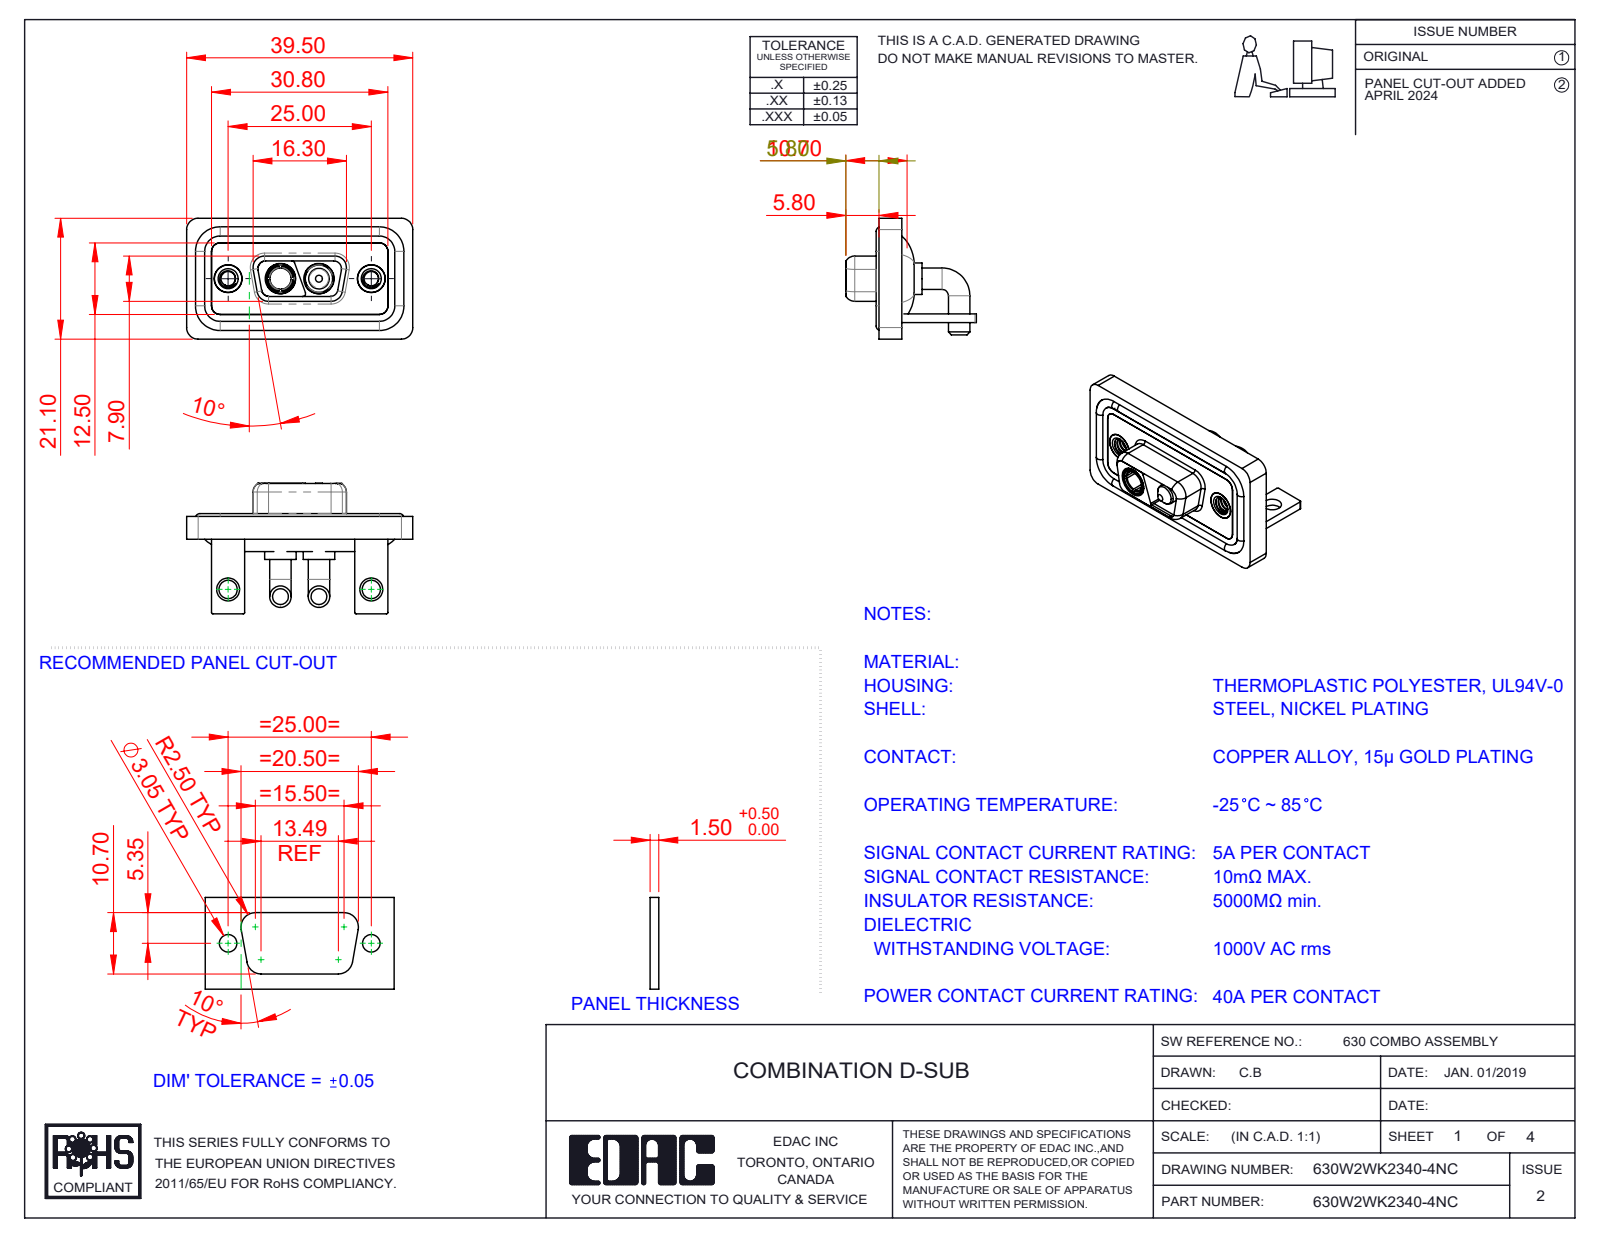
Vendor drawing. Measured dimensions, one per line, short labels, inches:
name: Power Socket_40A RA; Power Pin_40A RA; 630Combo Shell Front_09 Contacts; 630Combo Housing_2WK2 (+5 more)
written by: SolidWorks 2023 (CONFIG_CONTROL_DESIGN)
unit: in
bodies: 13 solids, 550 faces (164 planar, 257 cylindrical, 129 other)
size: 1.555 × 0.898 × 0.831
volume: 0.318 in³; area: 12.9 in²
holes: 4× ⌀0.191, 2× ⌀0.098, 2× ⌀0.126, 2× ⌀0.157, 2× ⌀0.159, 2× ⌀0.197, 2× ⌀0.209, 1× ⌀0.146
bosses: 4× ⌀0.148, 4× ⌀0.063, 2× ⌀0.217, 2× ⌀0.205, 2× ⌀0.195, 2× ⌀0.189, 2× ⌀0.187, 1× ⌀0.195
rounds: 19× R0.079, 18× R0.059, 16× R0.01, 8× R0.053, 8× R0.063, 7× R0.02, 4× R0.024, 4× R0.026
face distances: 0.016, 0.114, 0.059, 0.043, 0.146, 0.071, 0.031, 0.098, 0.063, 0.122
hole spacings: 0.36, 0.624, 0.984, 0.265
